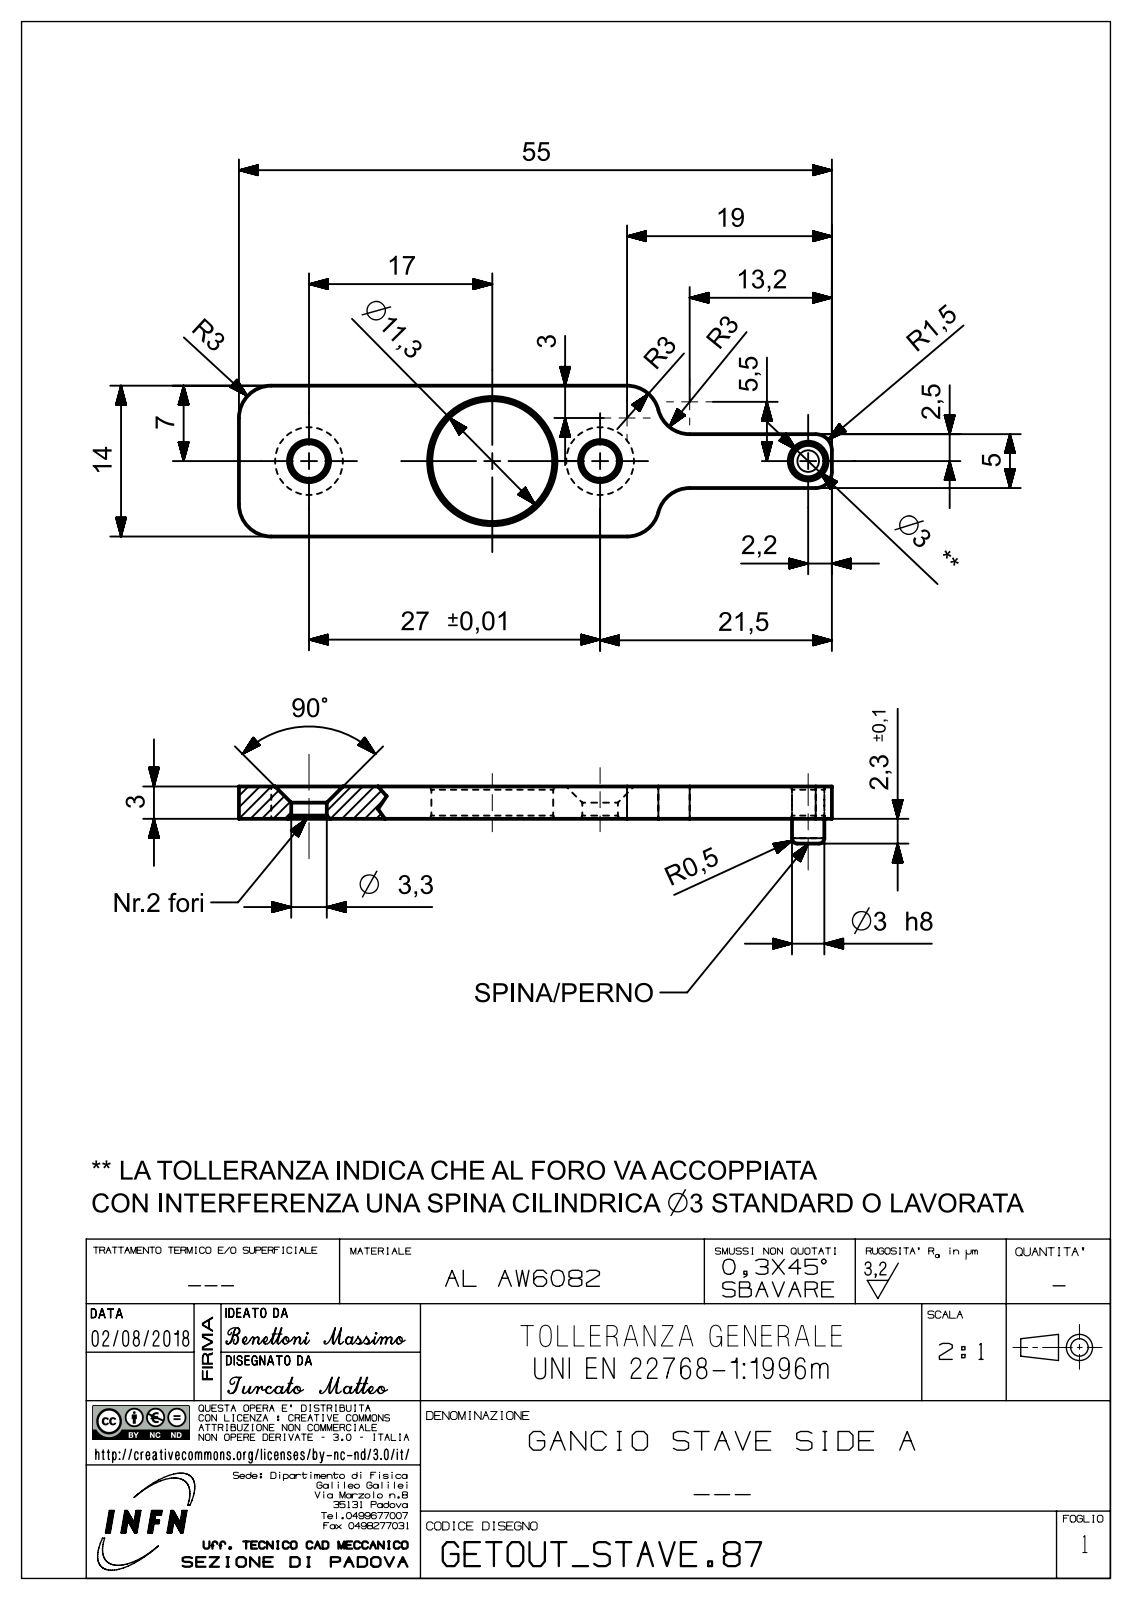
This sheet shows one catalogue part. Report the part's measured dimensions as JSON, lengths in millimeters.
{"part_name": "bezA730AE56ccyj", "step_written_by": "SIEMENS PLM Software NX 12.0 (AUTOMOTIVE_DESIGN)", "units": "millimeters", "bodies": {"solids": 1, "faces": 28, "planar": 8, "cylindrical": 12, "other": 8}, "overall_size": [55, 14, 3], "volume_mm3": 1452, "surface_area_mm2": 1546, "round_holes": [[3.3, 2], [3, 1], [11.3, 1]], "partial_cylinders_radius": [[3, 6], [1.5, 2]], "face_to_face_distances": [3, 14, 4.5, 9.5, 5, 55], "hole_center_spacings": [10, 17, 19.3, 27, 29.3, 46.3]}
